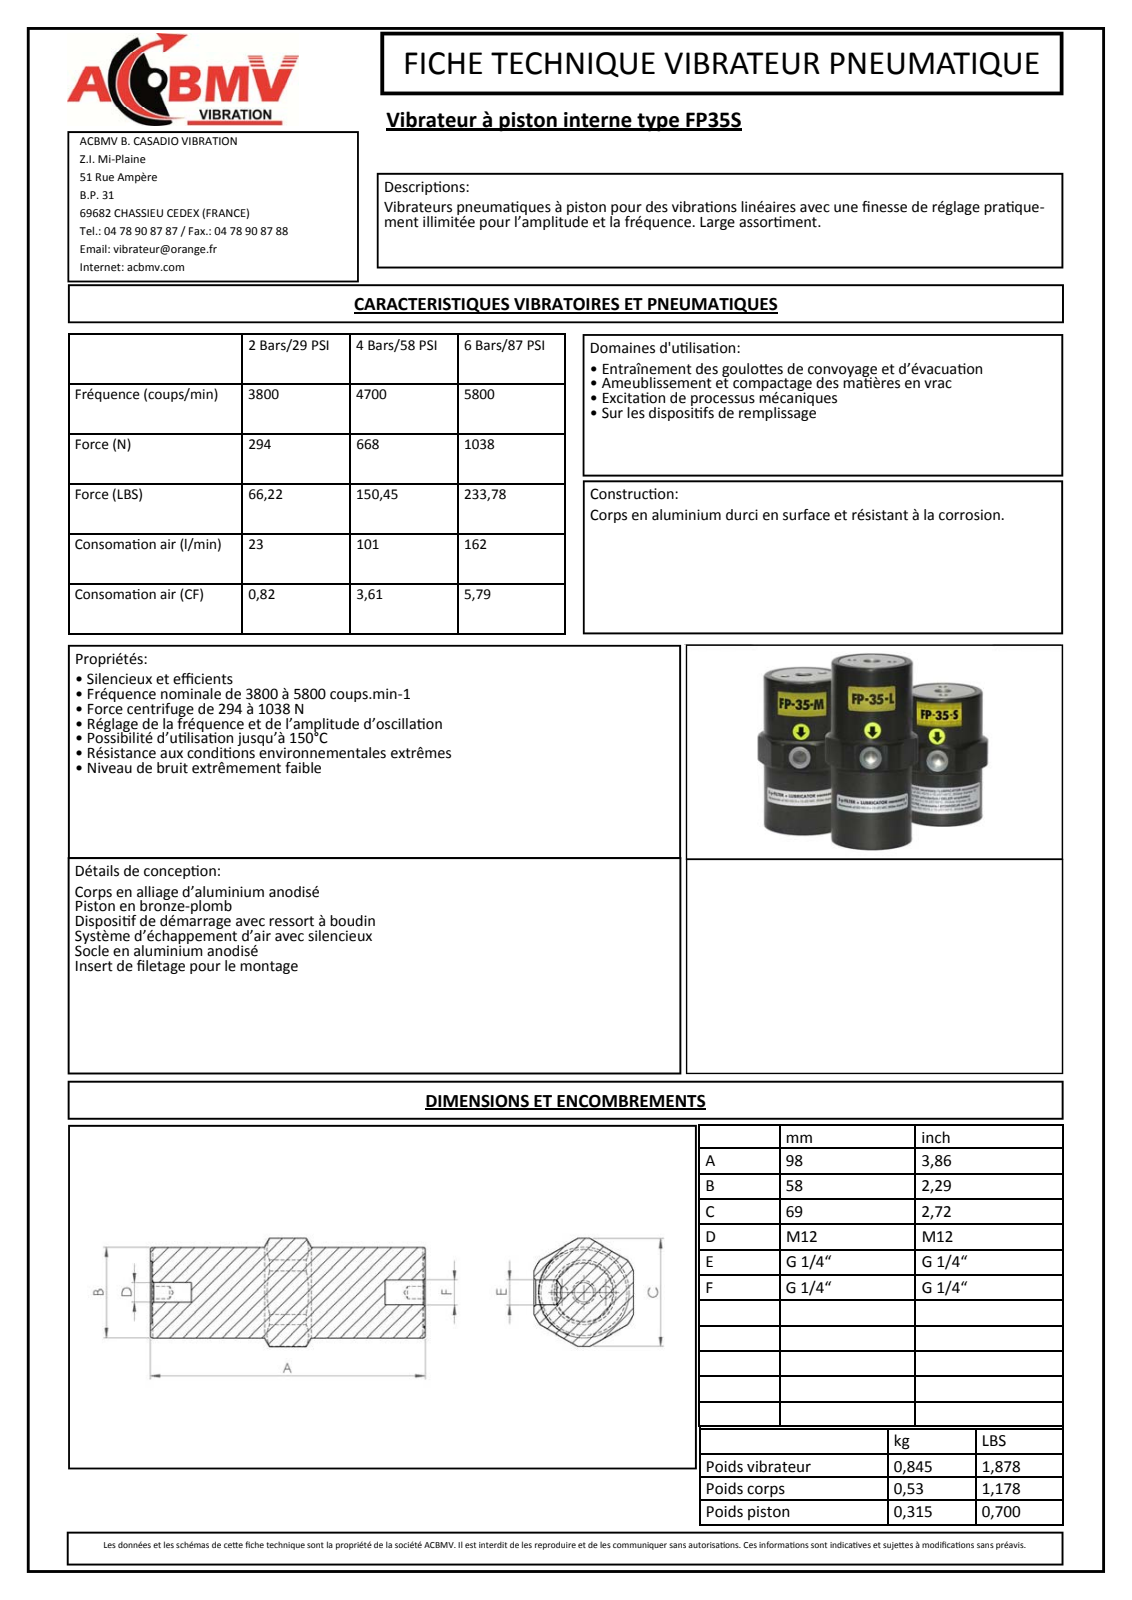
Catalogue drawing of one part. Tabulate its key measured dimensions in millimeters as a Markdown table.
| quantity | value |
| --- | --- |
| part name | 9035-10-M |
| STEP written by | Autodesk Inventor 2011 (CONFIG_CONTROL_DESIGN) |
| units | millimeters |
| bodies | 1 solid, 458 faces (186 planar, 56 cylindrical, 216 other) |
| overall size | 98 × 68.8 × 65 |
| volume | 268 317 mm³ |
| surface area | 26 825 mm² |
| round holes (diameter × count) | 6.2 × 2, 11.45 × 2, 10.11 × 1 |
| round bosses / shafts (diameter × count) | 58 × 1 |
| partial cylindrical surfaces (radius × count) | 19.5 × 1, 28.8 × 1, 29.08 × 1, 29.1 × 1, 34.4 × 1 |
| main face-to-face distances | 97.5, 0.5, 98, 65, 84.3, 83.8, 13.7, 19, 18.5, 65.3 |
| hole center spacings | 15, 30 |
